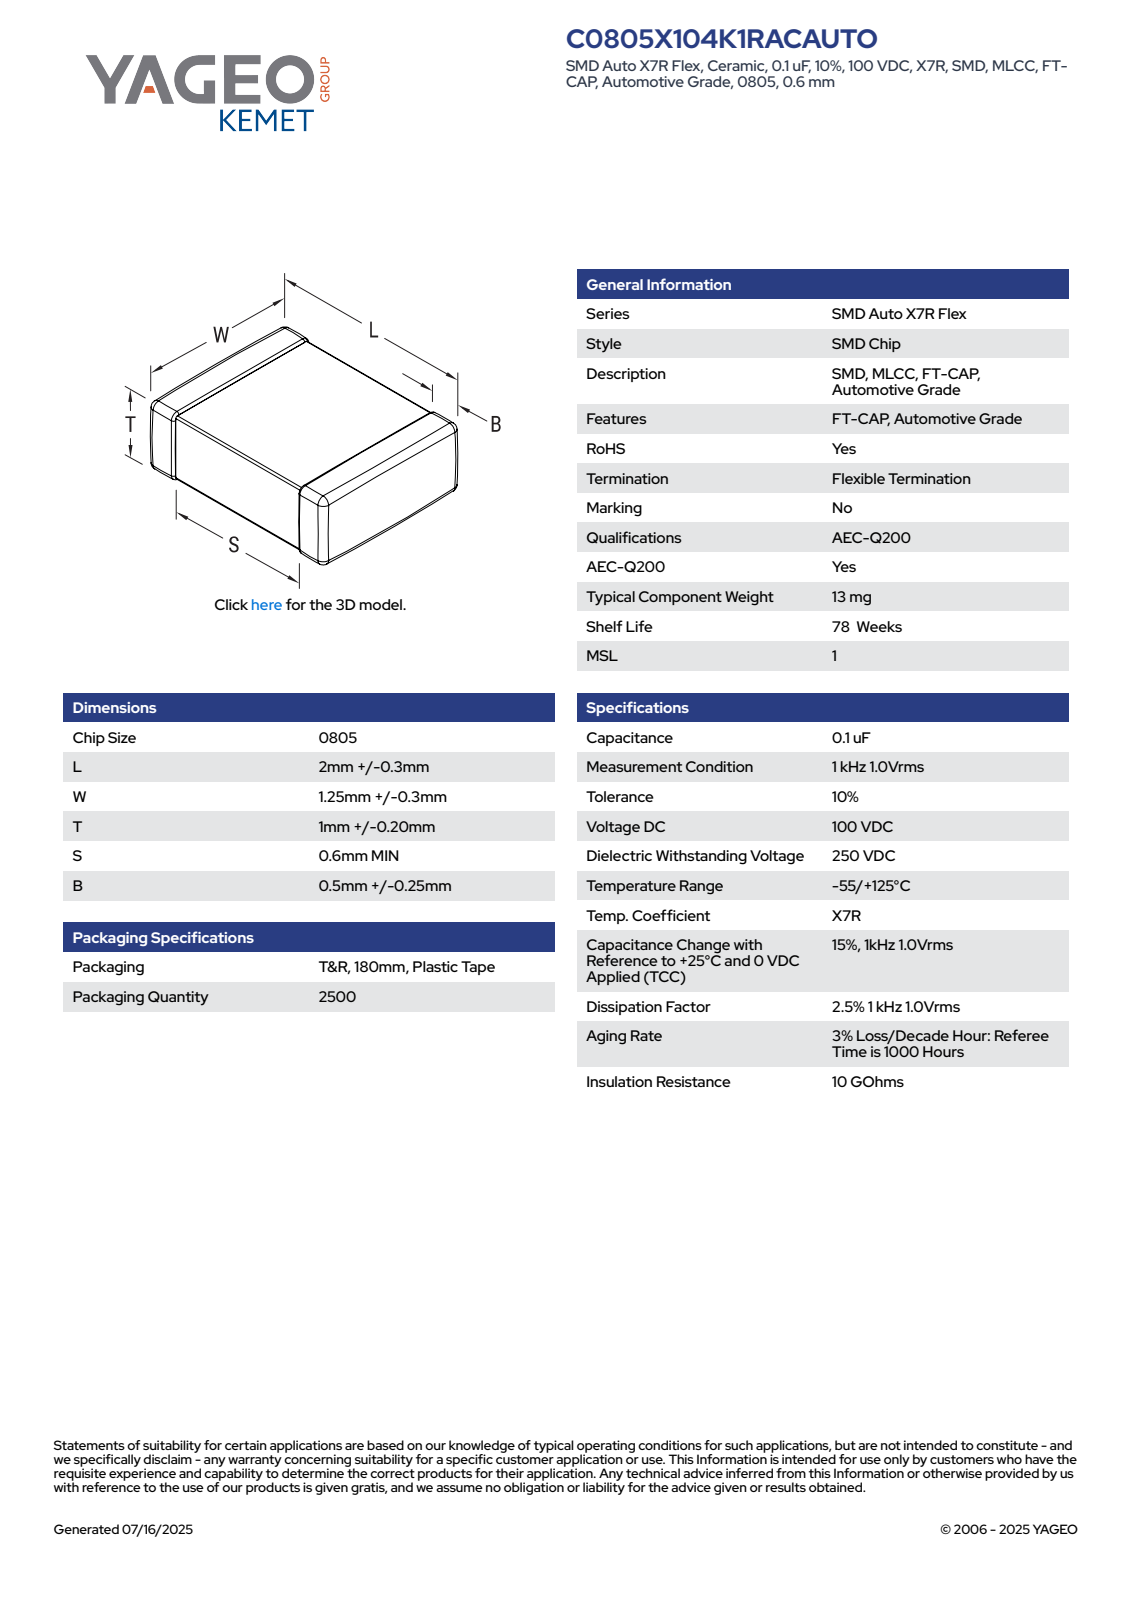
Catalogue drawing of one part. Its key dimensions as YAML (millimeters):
part_name: "CCS_CCSTD_0805_L2.3W1.55T1.2B0.5"
step_written_by: "SolidWorks 2021 (AUTOMOTIVE_DESIGN)"
units: millimeters
bodies: {solids: 4, faces: 125, planar: 71, cylindrical: 38, other: 16}
overall_size: [2.3, 1.55, 1.2]
volume: 4
surface_area: 16
face_to_face_distances: [1.17, 1.2, 1.52, 2.3, 1.55, 1.14, 1.49, 1.06, 1.24, 1.01]
